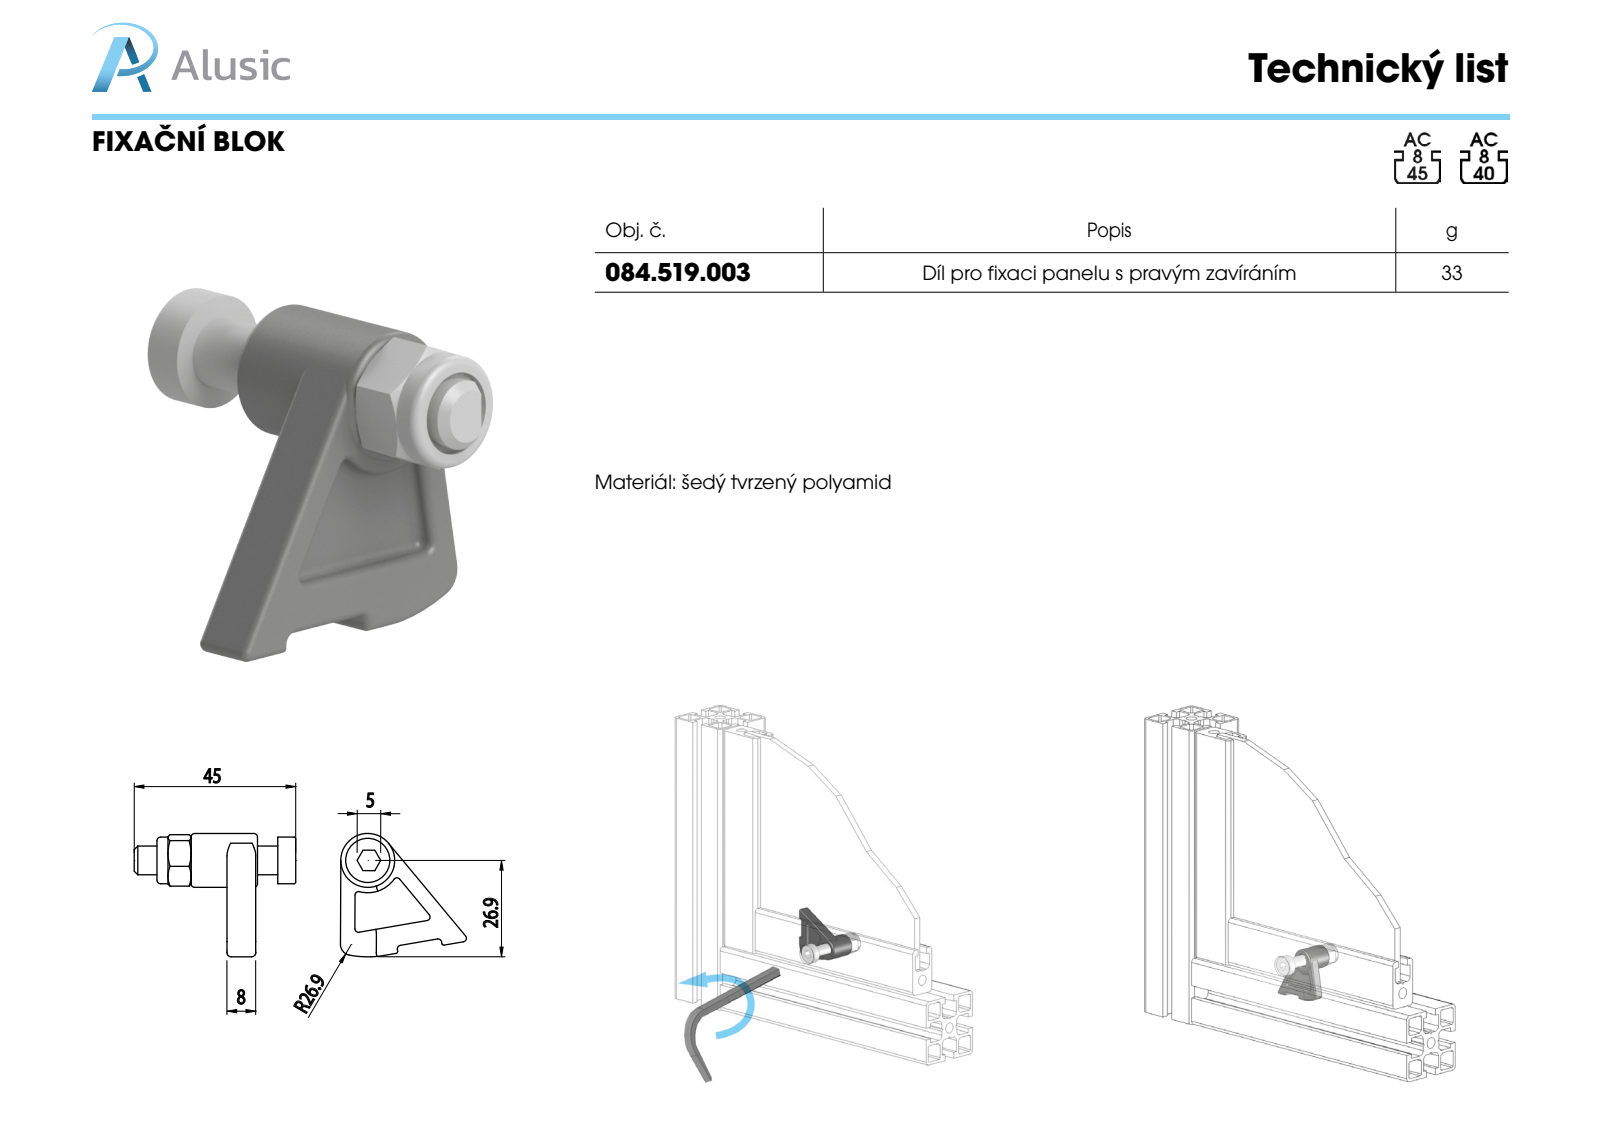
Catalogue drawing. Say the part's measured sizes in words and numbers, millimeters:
The part is named "985-A2; 084.519.003; 084.519.005; 084.519.003L". Its 3-D file was written by "SolidWorks 2011 (CONFIG_CONTROL_DESIGN)". It is 3 solids with 221 faces: 43 planar, 76 cylindrical and 102 other. Overall it measures 45 by 34.93 by 34.36 millimeters. Its volume is 9 001 cubic millimeters and its surface area 5 720 square millimeters. Round holes: 1 of diameter 6.8, 1 of diameter 8, 1 of diameter 9.43. Round bosses or shafts: 1 of diameter 15, 1 of diameter 13. Partial cylindrical surfaces (rounded edges, fillets, slot ends): 33 of radius 1, 2 of radius 0.5, 1 of radius 3, 1 of radius 4.1, 1 of radius 9, 1 of radius 26.85. The main face-to-face distances are 2.5, 5.5, 3, 8.5, 6, 0.5, 5, 8, 25.83, 10.
